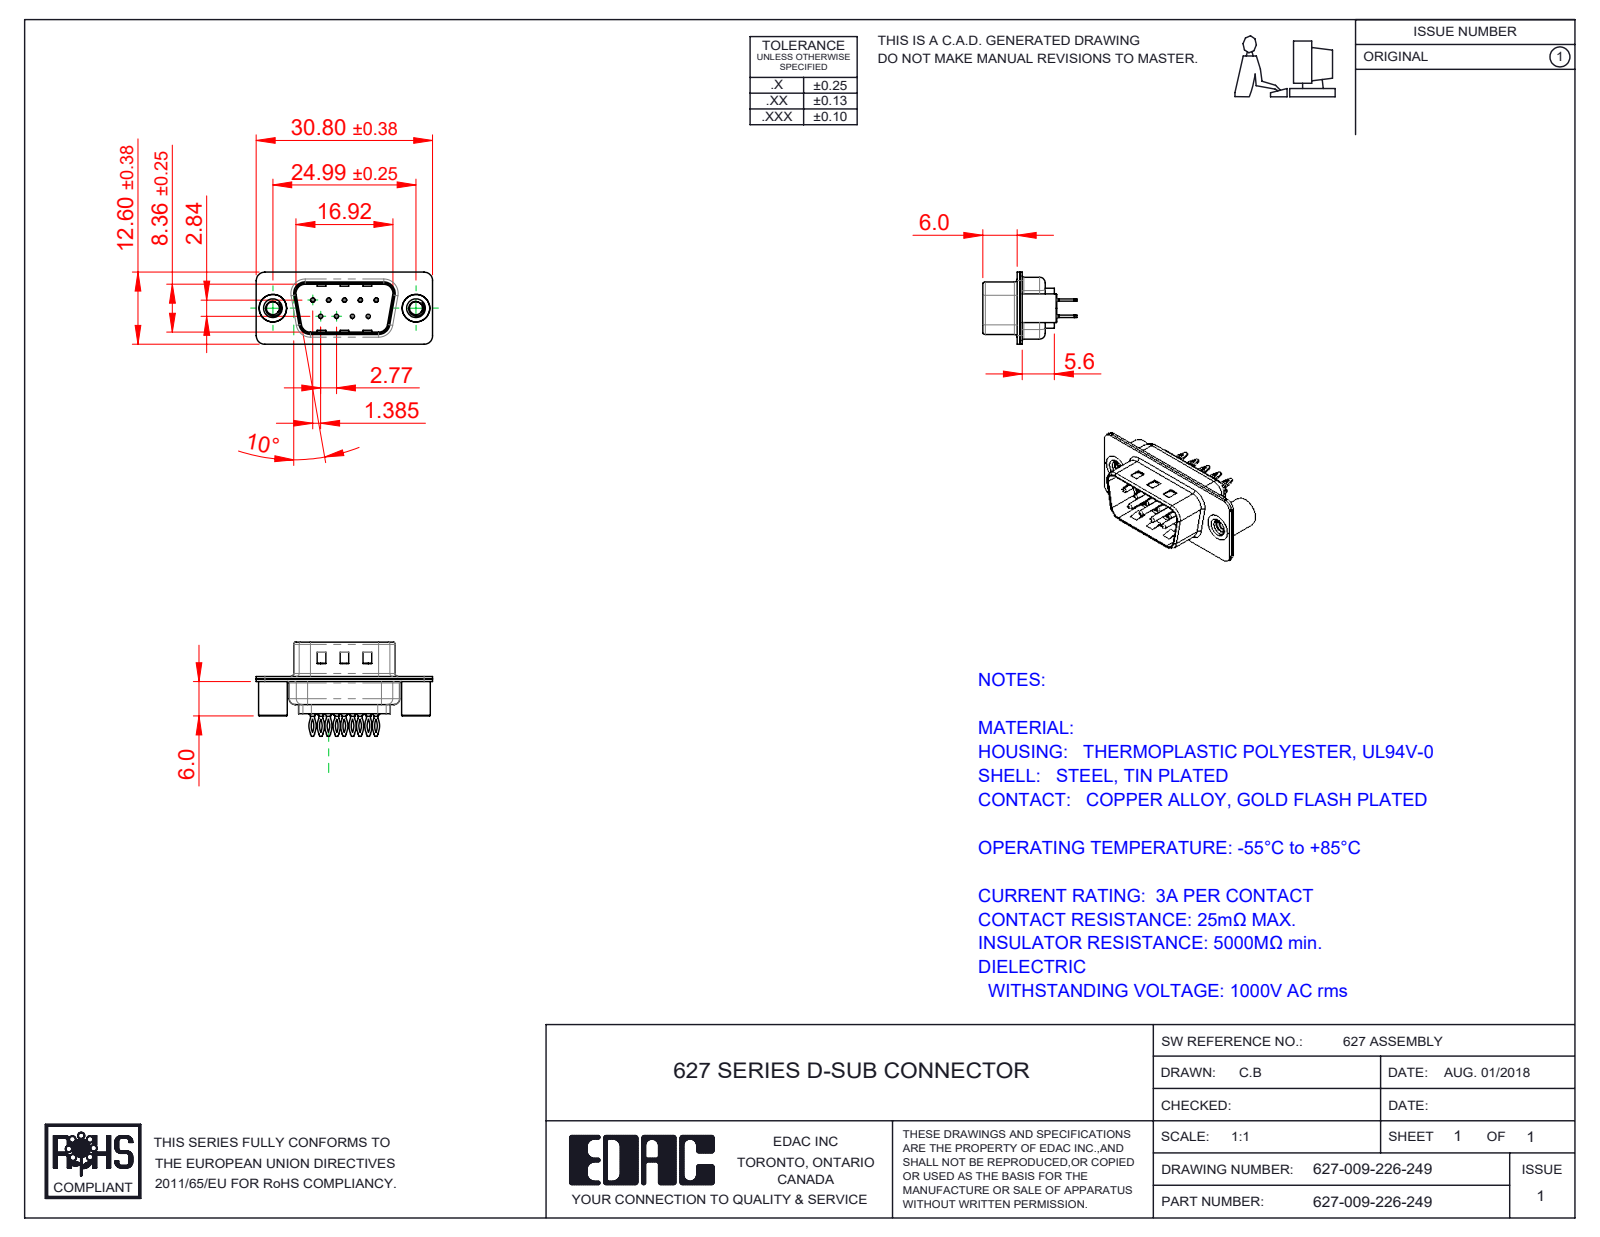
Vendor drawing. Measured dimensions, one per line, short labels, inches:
name: 627 Housing_09 LP; 627 Shell Front_09 Contacts; 627 Shell Rear_09 Contacts; 627 Contact Row 2_26L (+3 more)
written by: SolidWorks 2020 (CONFIG_CONTROL_DESIGN)
unit: in
bodies: 14 solids, 1010 faces (287 planar, 428 cylindrical, 295 other)
size: 1.213 × 0.648 × 0.496
volume: 0.086 in³; area: 6.349 in²
holes: 9× ⌀0.014, 9× ⌀0.043, 9× ⌀0.063, 2× ⌀0.089, 2× ⌀0.157, 2× ⌀0.189
bosses: 9× ⌀0.079, 9× ⌀0.059, 9× ⌀0.03, 2× ⌀0.197, 2× ⌀0.193
rounds: 18× R0.059, 18× R0.115, 18× R0.131, 12× R0.079, 8× R0.02, 8× R0.063, 4× R0.01, 4× R0.024
face distances: 0.016, 0.018, 0.035, 0.032, 0.377, 0.055, 0.345, 0.256, 0.02, 0.059
hole spacings: 0.124, 0.109, 0.218, 0.198, 0.198, 0.327, 0.294, 0.295
